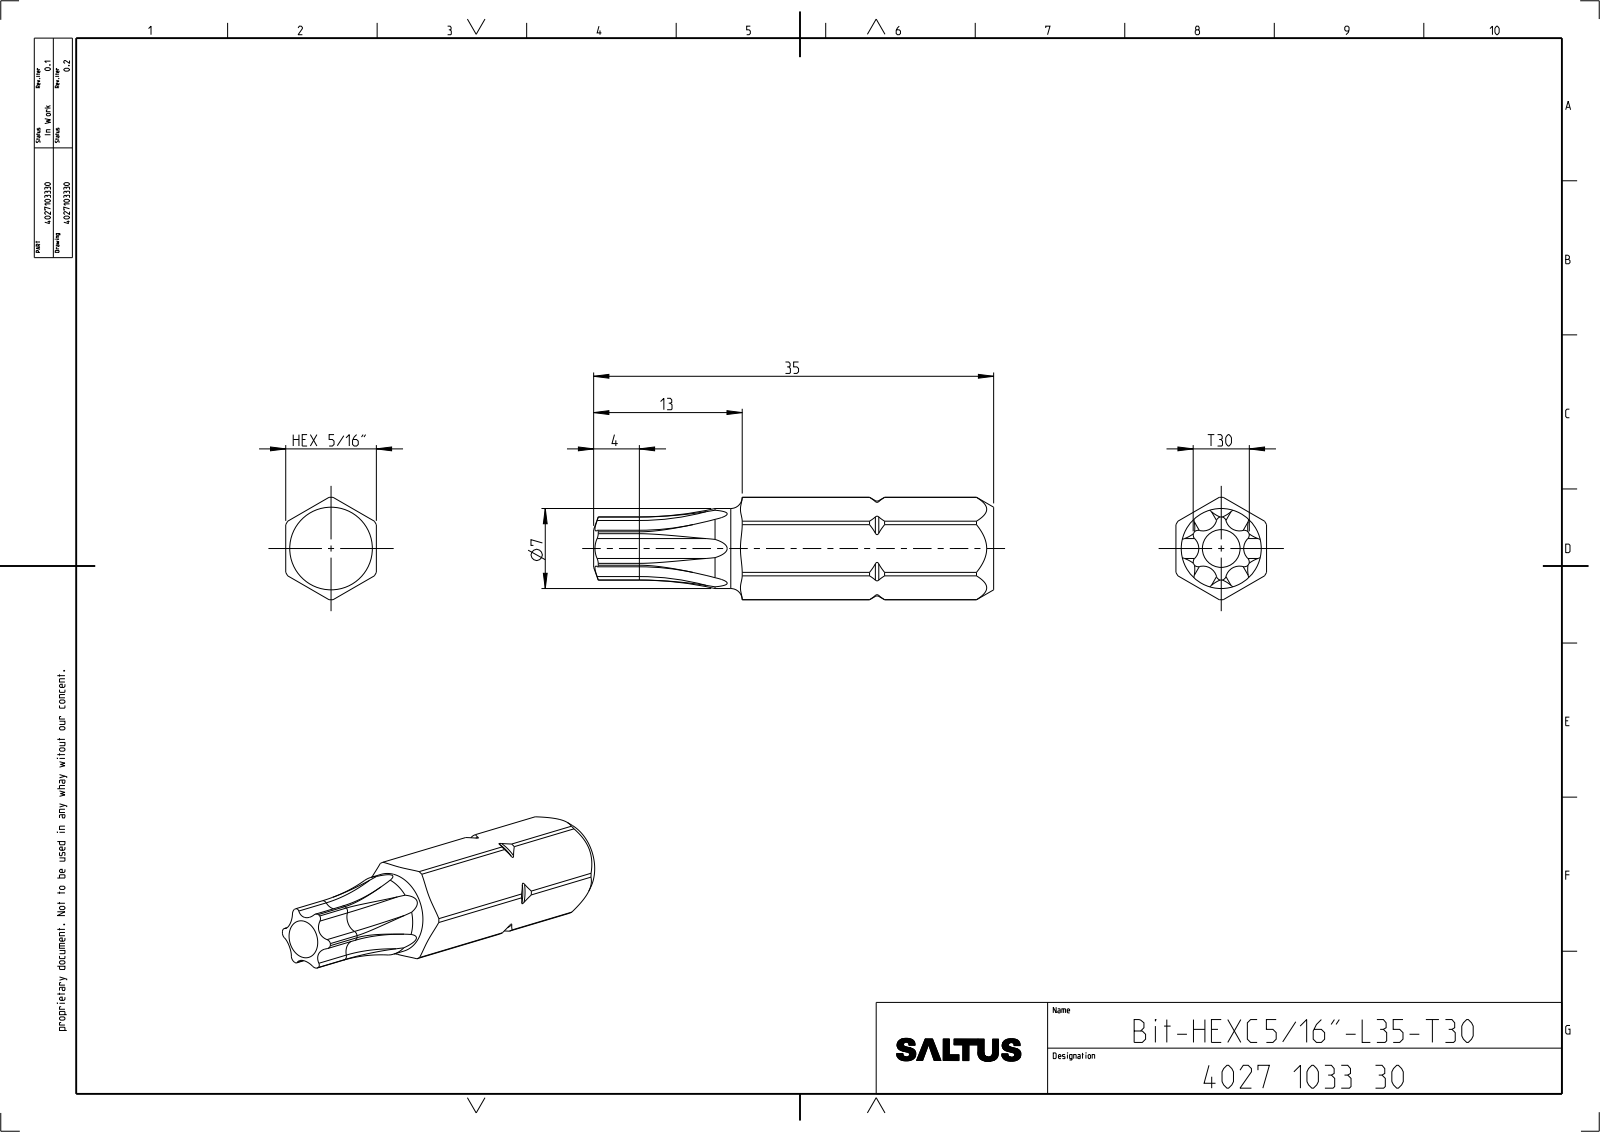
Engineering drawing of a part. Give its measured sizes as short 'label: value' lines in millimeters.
name: 4027103330
written by: CREO PARAMETRIC BY PTC INC, 2022414 (CONFIG_CONTROL_DESIGN)
unit: mm
bodies: 1 solid, 94 faces (8 planar, 38 cylindrical, 48 other)
size: 35 × 8.96 × 7.93
volume: 1 500 mm³; area: 921 mm²
bosses: 1× ⌀7
rounds: 10× R0.42, 6× R1.22, 1× R2.76, 1× R4.48
face distances: 7.92, 35
